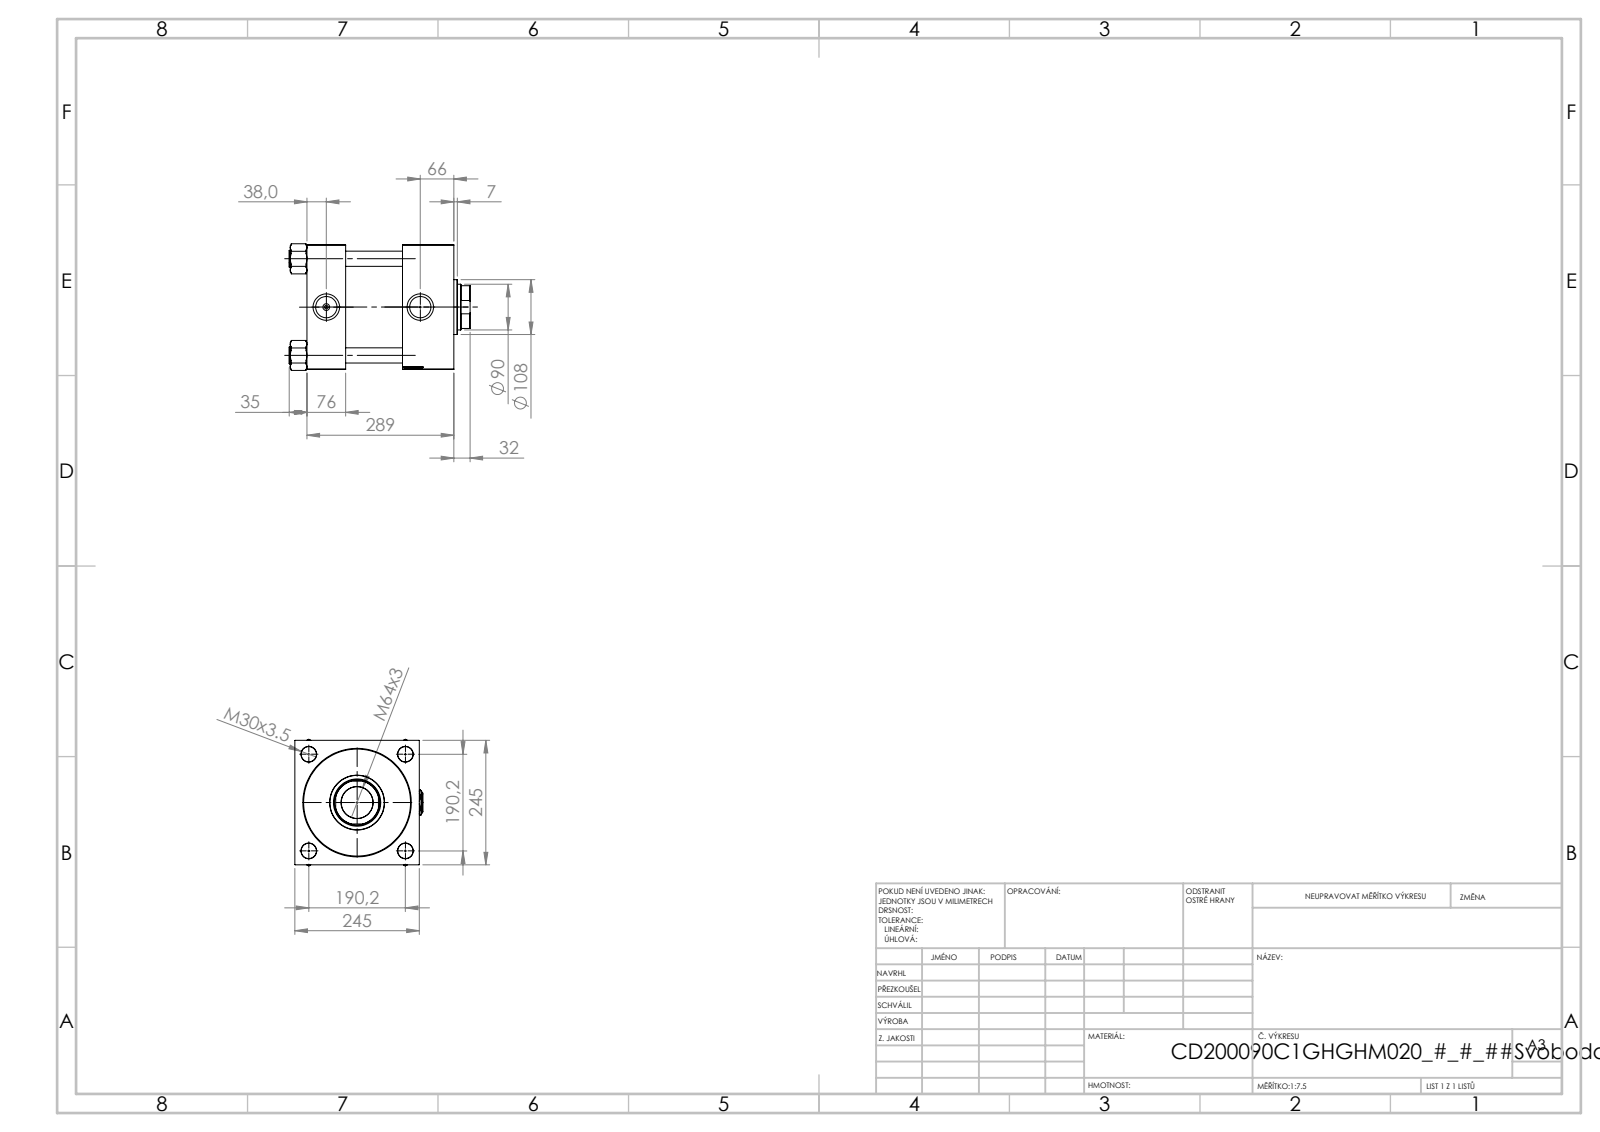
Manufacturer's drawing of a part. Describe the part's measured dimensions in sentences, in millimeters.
The part is named "Zatka_pro_OIL_PORT; V215CD_VCP_C; V215CD_VC_C; V215CD_C_TYCINKA (+2 more)". Its 3-D file was written by "SolidWorks 2019 (CONFIG_CONTROL_DESIGN)". It is 12 solids with 1243 faces: 597 planar, 90 cylindrical and 556 other. Overall it measures 356 by 252 by 249.44 millimeters. Its volume is 13 380 000 cubic millimeters and its surface area 1 048 000 square millimeters. Round holes: 4 of diameter 30, 2 of diameter 7, 2 of diameter 41.92, 2 of diameter 52, 1 of diameter 62.5, 1 of diameter 90, 1 of diameter 93, 1 of diameter 146, 1 of diameter 200, 1 of diameter 210.5. Round bosses or shafts: 4 of diameter 33, 1 of diameter 206, 1 of diameter 108. Partial cylindrical surfaces (rounded edges, fillets, slot ends): 1 of radius 44. The main face-to-face distances are 245, 76, 289, 213, 260.3, 184.3, 28.7, 188, 112, 72.3. The hole center spacings are 134.49, 190.2, 268.98, 185.
